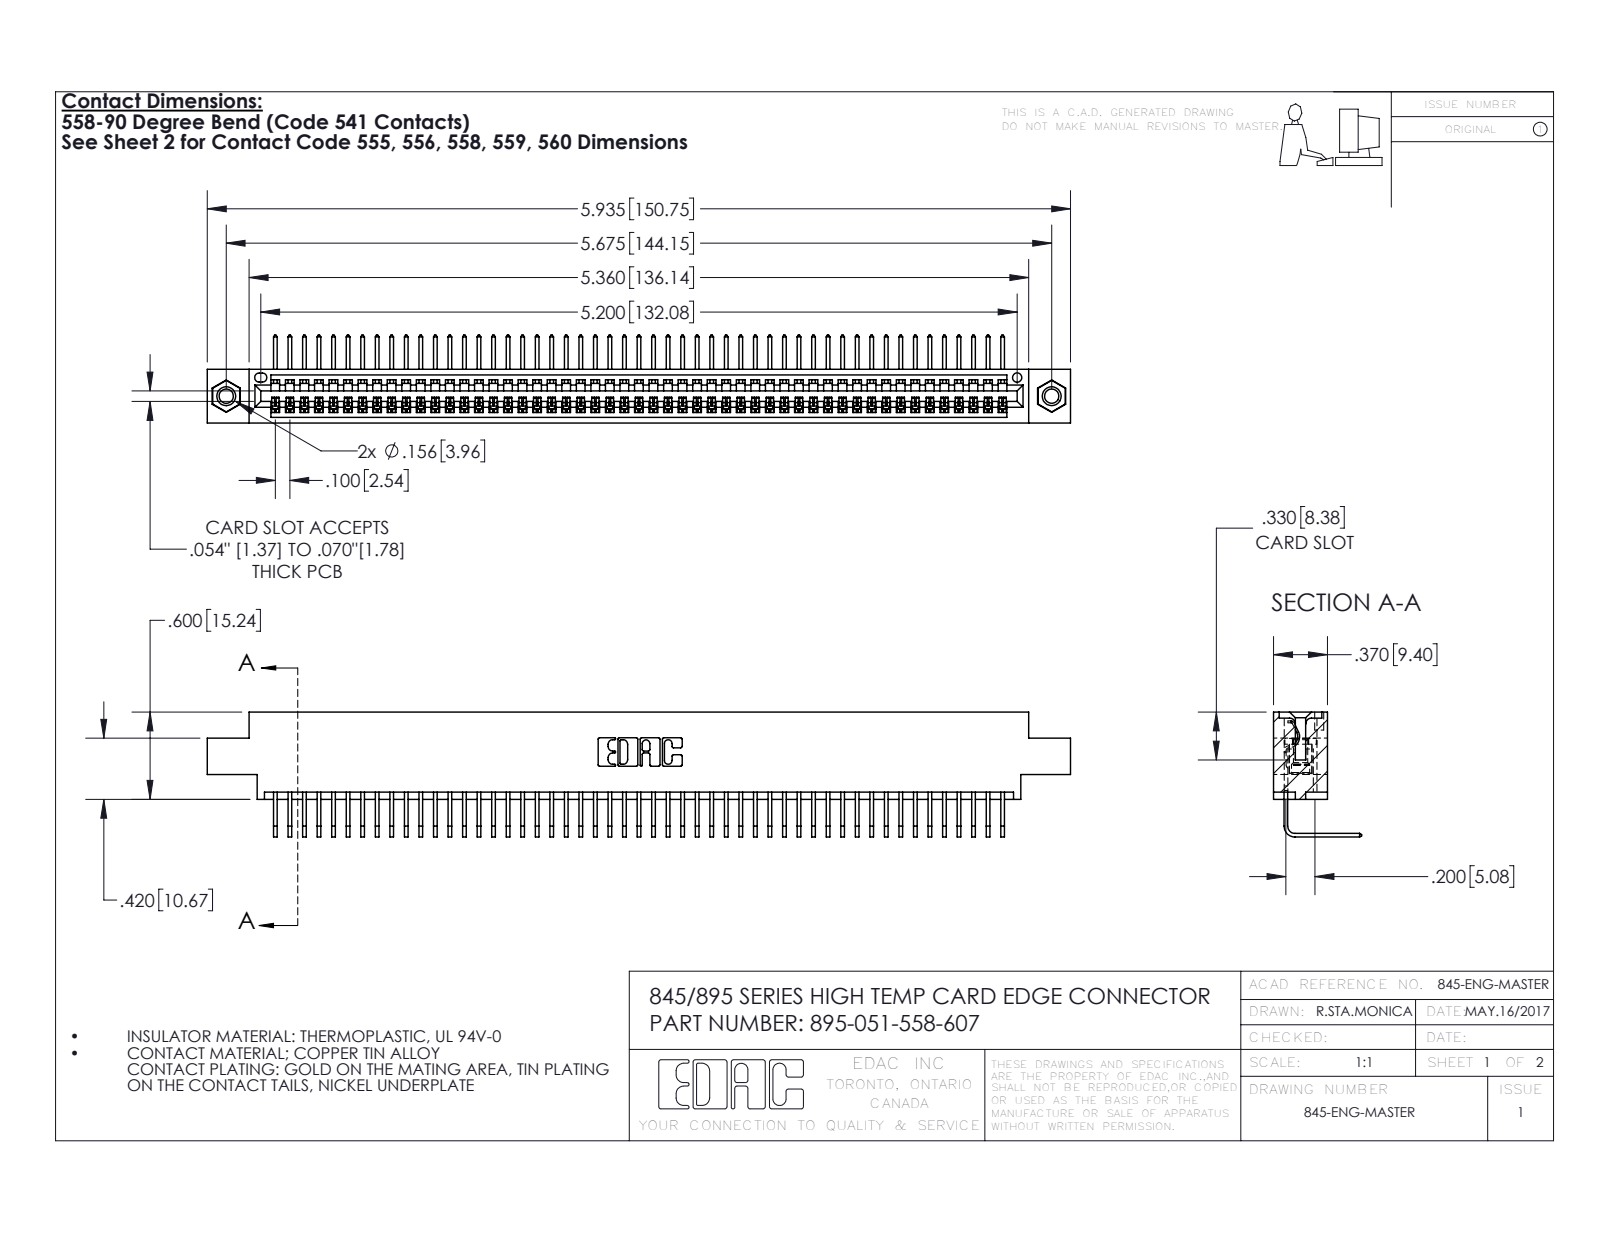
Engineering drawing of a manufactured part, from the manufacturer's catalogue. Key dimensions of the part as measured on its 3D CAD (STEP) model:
Part name (STEP PRODUCT): 345 Part_0.170 Offset - 0.156 Dia-TI; 395-051-558-607; 345-292-001_558 Tail - 2; 345-250-001_345-250-005-103
STEP written by: SolidWorks 2016 (CONFIG_CONTROL_DESIGN)
Units: inches
Bodies: 54 solids, 3250 faces (2258 planar, 976 cylindrical, 16 other)
Overall size (bounding box): 5.935 × 0.859 × 0.605
Volume: 0.881 in³ · Surface area: 31.72 in²
Round holes (diameter × count): ⌀0.098 ×2, ⌀0.125 ×2, ⌀0.156 ×2, ⌀0.064 ×1
Round bosses / shafts (diameter × count): ⌀0.155 ×2
Partial cylindrical surfaces — rounded edges, fillets, slot ends (radius × count): R0.006 ×102, R0.01 ×22, R0.007 ×6, R0.031 ×6, R0.026 ×3, R0.031 ×2, R0.04 ×2, R0.014 ×1
Main face-to-face distances: 0.072, 0.298, 0.37, 0.2, 0.098, 0.272, 0.025, 0.225, 0.175, 0.149
Hole centre spacings: 0.27, 5.439, 5.675
